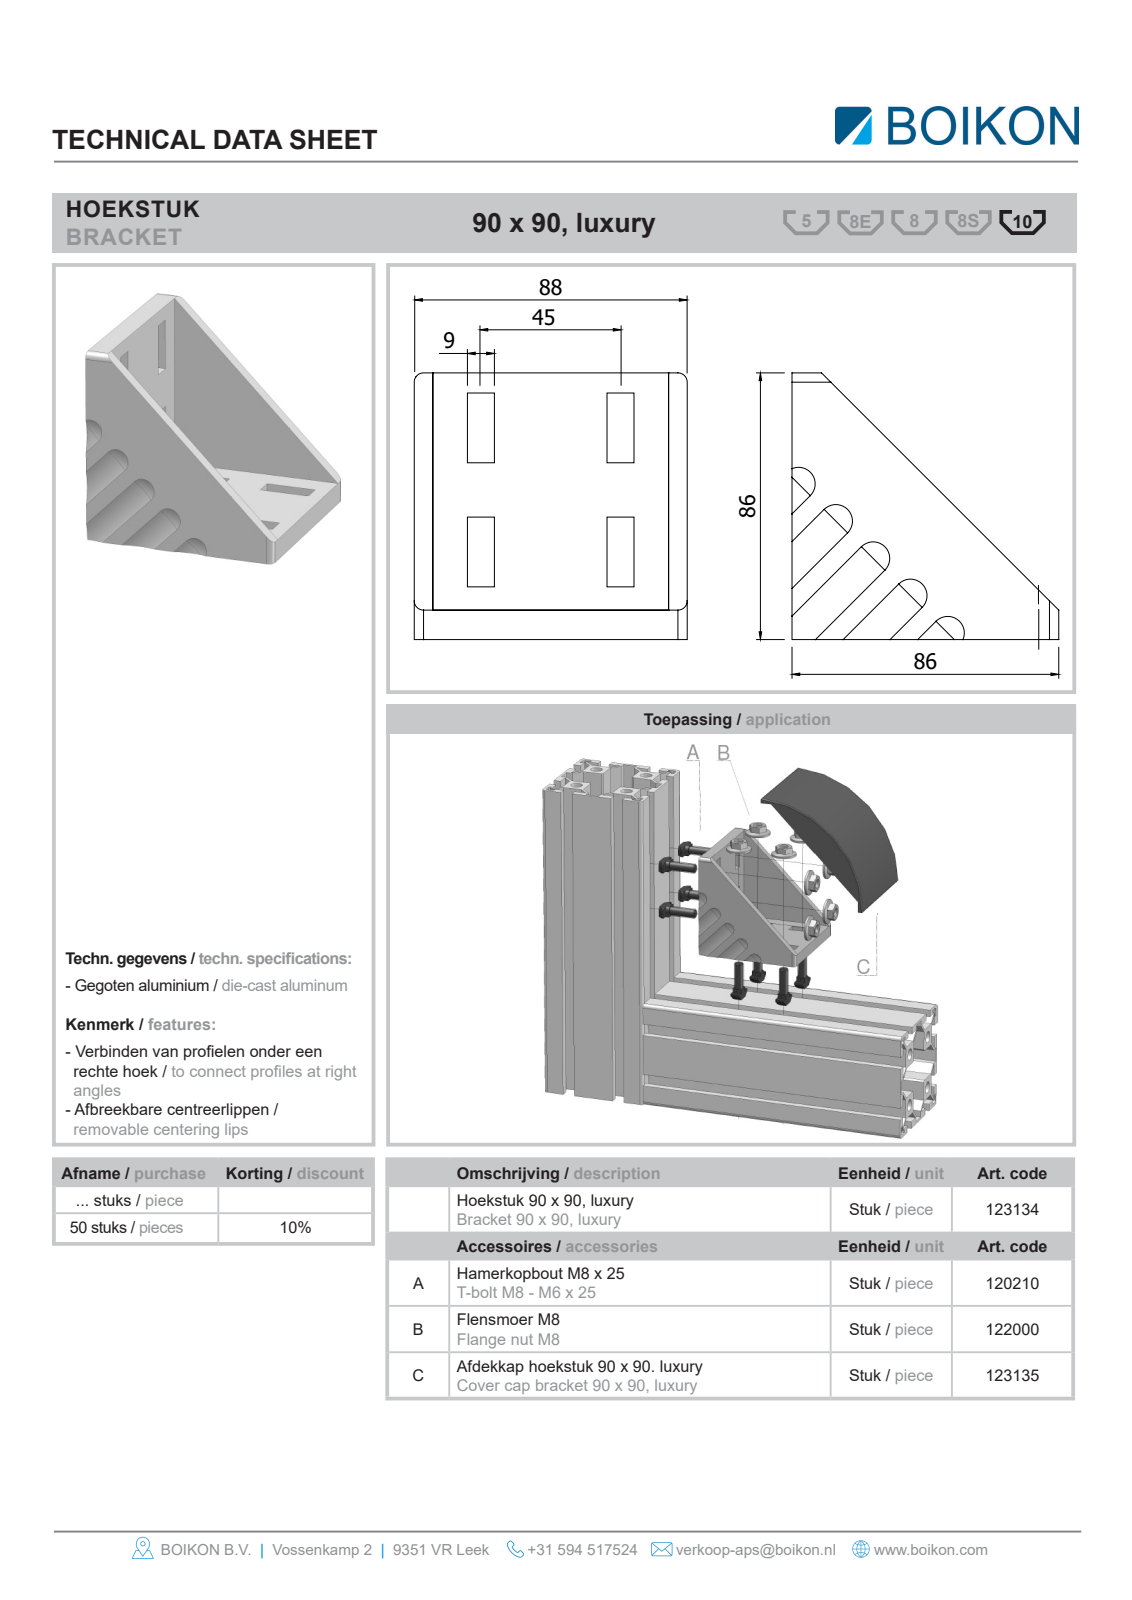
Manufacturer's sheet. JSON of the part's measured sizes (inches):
{"part_name": "Root; 123134HOEKSTUK 90X90 LUXURYBOIKON; 123135AFDEKKAP HOEKSTUK 90X90 LUXURYBOIKON; 122000Flensmoer M8BOIKON (+1 more)", "step_written_by": "HiCAD 2013 1802.4 Build 509 (AUTOMOTIVE_DESIGN)", "units": "inches", "bodies": {"solids": 18, "faces": 763, "planar": 541, "cylindrical": 122, "other": 100}, "overall_size": [4.014, 3.994, 3.465], "volume_in3": 14.77, "surface_area_in2": 148.2, "round_holes": [[0.315, 8]], "round_bosses_or_shafts": [[0.827, 8], [0.255, 8]], "partial_cylinders_radius": [[0.039, 34], [0.016, 16], [0.512, 10], [0.197, 8], [0.382, 8], [0.118, 4], [3.386, 1], [3.543, 1]], "face_to_face_distances": [0.374, 0.236, 3.228, 3.465, 2.992, 0.224, 3.24, 3.004, 1.772, 3.386], "hole_center_spacings": [1.575, 1.772, 2.37]}
